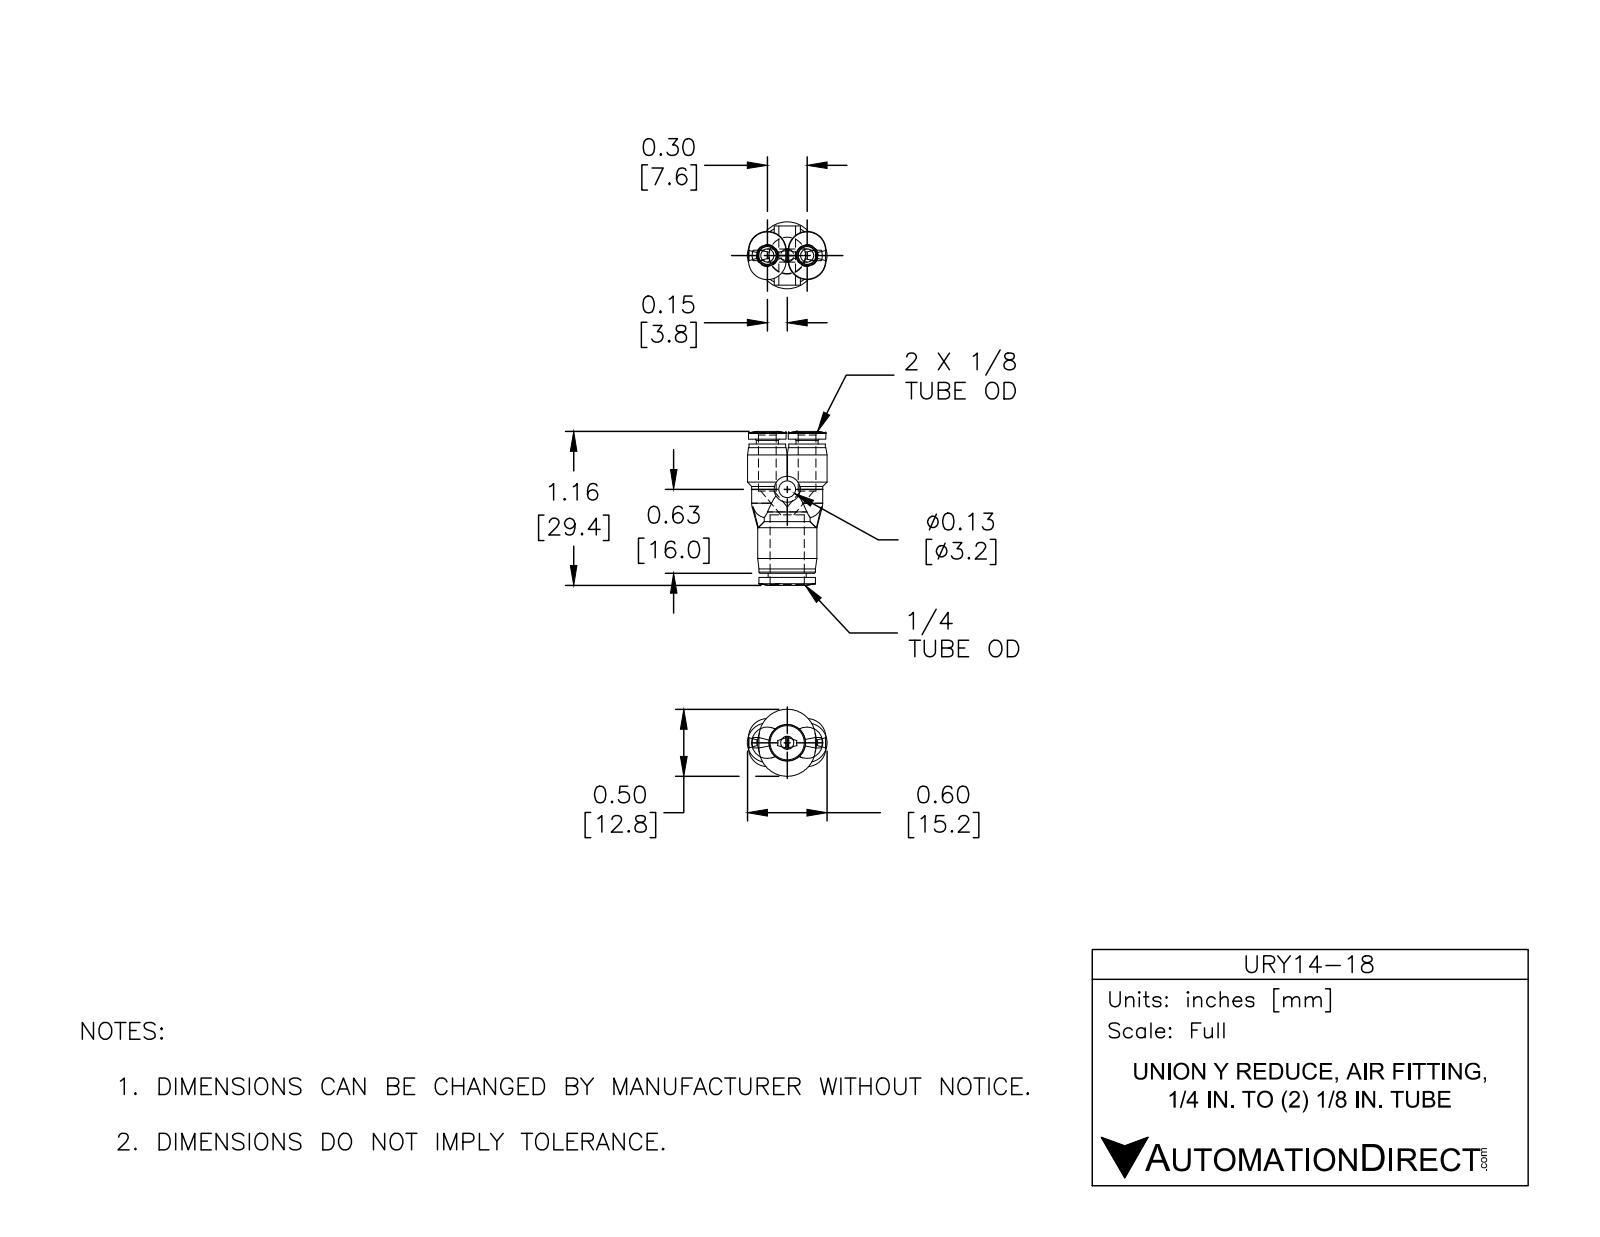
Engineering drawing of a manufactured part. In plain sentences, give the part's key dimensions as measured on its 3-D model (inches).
The part is named "URY14-18". Its 3-D file was written by "SolidWorks 2015 (CONFIG_CONTROL_DESIGN)". It is 1 solid with 133 faces: 26 planar, 42 cylindrical and 65 other. Overall it measures 1.159 by 0.598 by 0.504 inches. Its volume is 0.114 cubic inches and its surface area 3.656 square inches. Round holes: 2 of diameter 0.134, 1 of diameter 0.126, 1 of diameter 0.258. Round bosses or shafts: 2 of diameter 0.299, 2 of diameter 0.276, 2 of diameter 0.165, 1 of diameter 0.445, 1 of diameter 0.425, 1 of diameter 0.354, 1 of diameter 0.287, 1 of diameter 0.197. Partial cylindrical surfaces (rounded edges, fillets, slot ends): 4 of radius 0.142, 2 of radius 0.118, 2 of radius 0.213. The main face-to-face distances are 1.039, 1.004, 0.035, 0.031, 0.972, 1.008, 0.471, 0.439, 0.533, 0.569. The hole center spacings are 0.15, 0.299.
